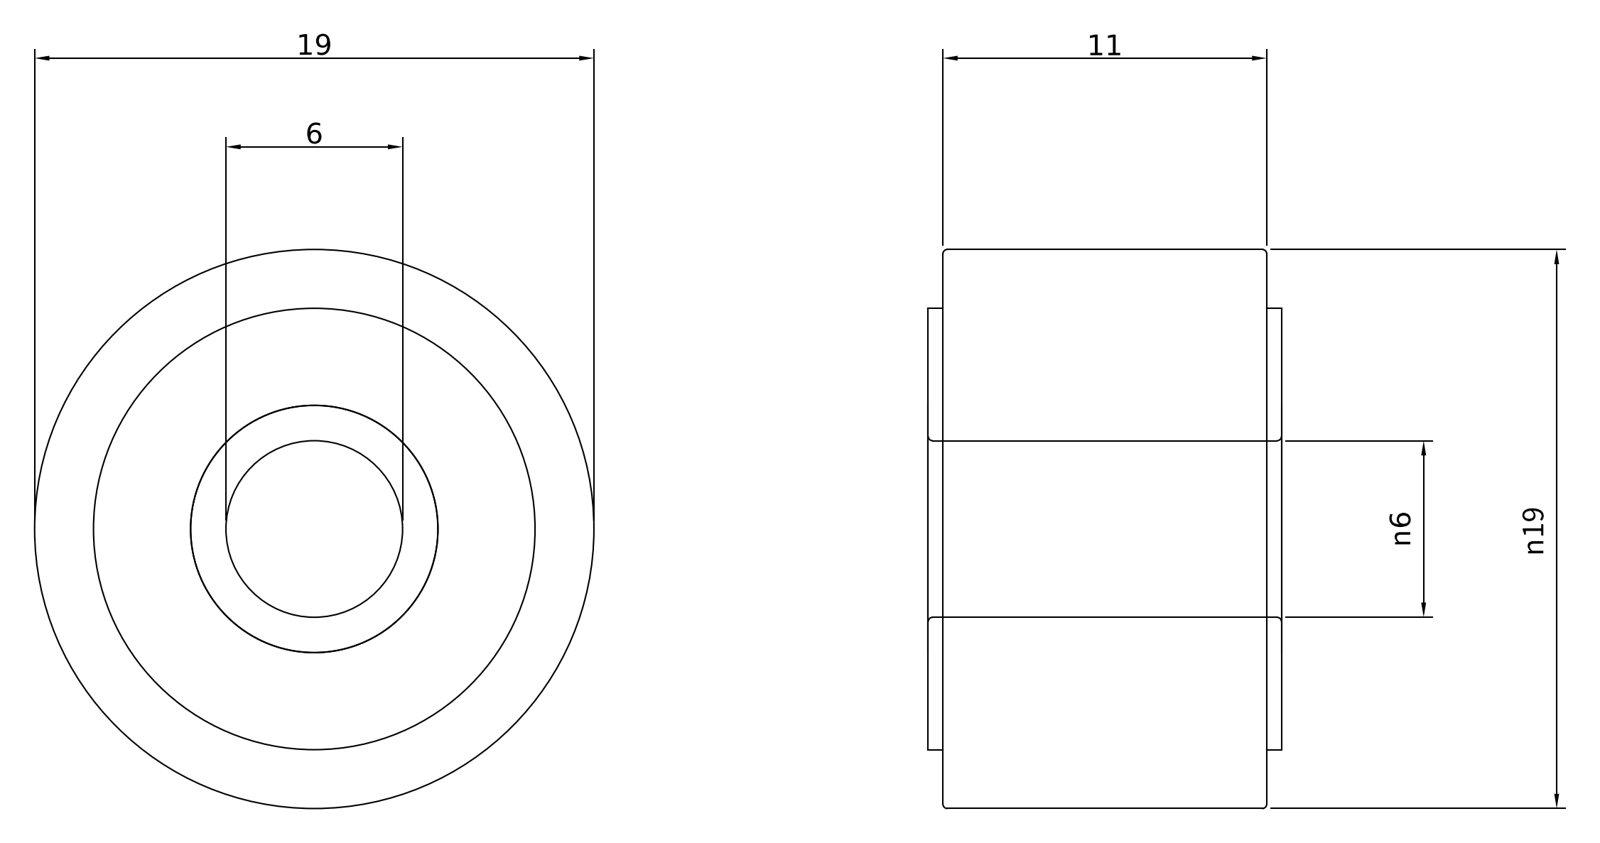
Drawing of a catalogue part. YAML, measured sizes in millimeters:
part_name: "DM80CUNATR6"
step_written_by: "Autodesk Inventor 2022 (AUTOMOTIVE_DESIGN)"
units: millimeters
bodies: {solids: 1, faces: 20, planar: 8, cylindrical: 8, other: 4}
overall_size: [19, 19, 12]
volume: 2955
surface_area: 1430
round_holes:
  - {diameter: 6, count: 1}
  - {diameter: 8.4, count: 1}
round_bosses_or_shafts:
  - {diameter: 19, count: 1}
  - {diameter: 15, count: 1}
  - {diameter: 8.4, count: 1}
face_to_face_distances: [0.5, 11.5, 12, 11]
